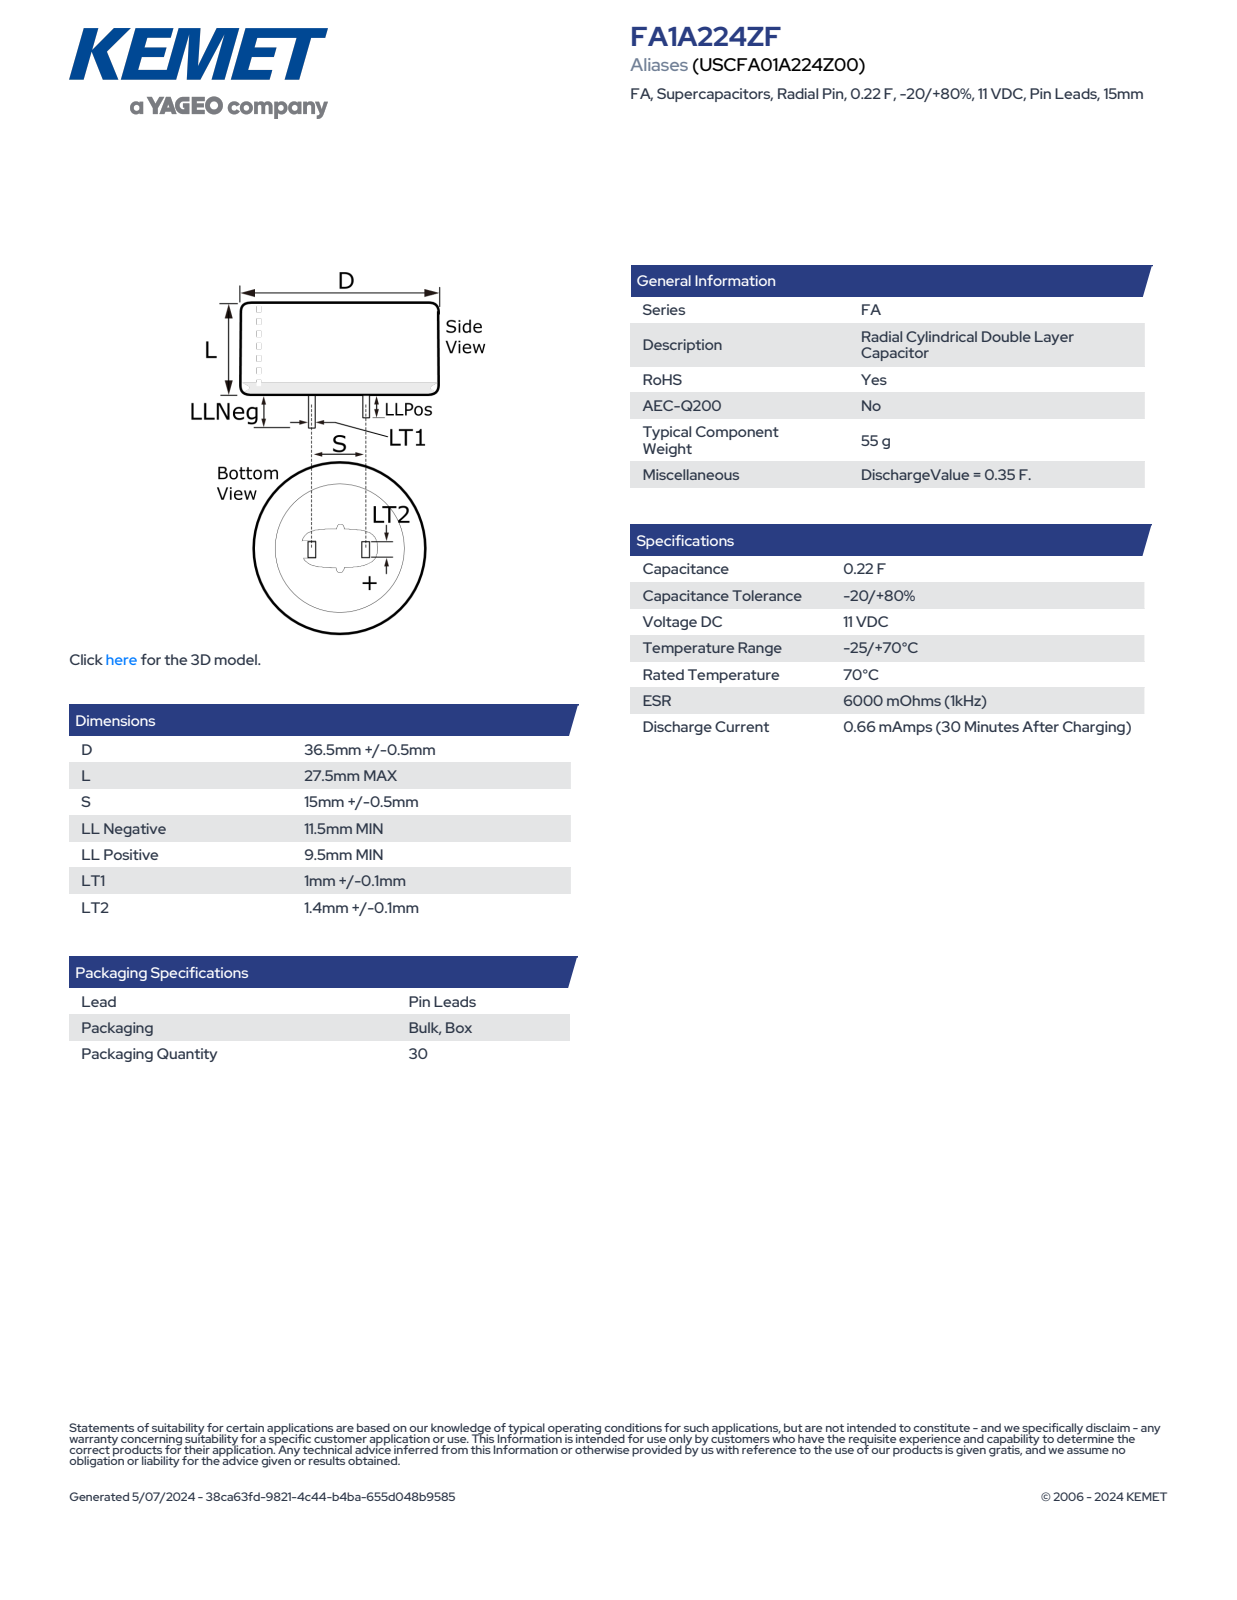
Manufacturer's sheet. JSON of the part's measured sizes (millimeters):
{"part_name": "CDR_LPLLN_D37L27.5S15LLNEG11.5LLPOS9.5LT11.1LT21.5", "step_written_by": "SolidWorks 2014 (AUTOMOTIVE_DESIGN)", "units": "millimeters", "bodies": {"solids": 1, "faces": 78, "planar": 70, "cylindrical": 4, "other": 4}, "overall_size": [39, 37, 37], "volume_mm3": 29450, "surface_area_mm2": 5277, "round_bosses_or_shafts": [[37, 1]], "partial_cylinders_radius": [[18.51, 1]], "face_to_face_distances": [27.5, 1.1, 15, 1.5, 16.1, 13.9, 27.49, 11.5, 38.99, 39]}
